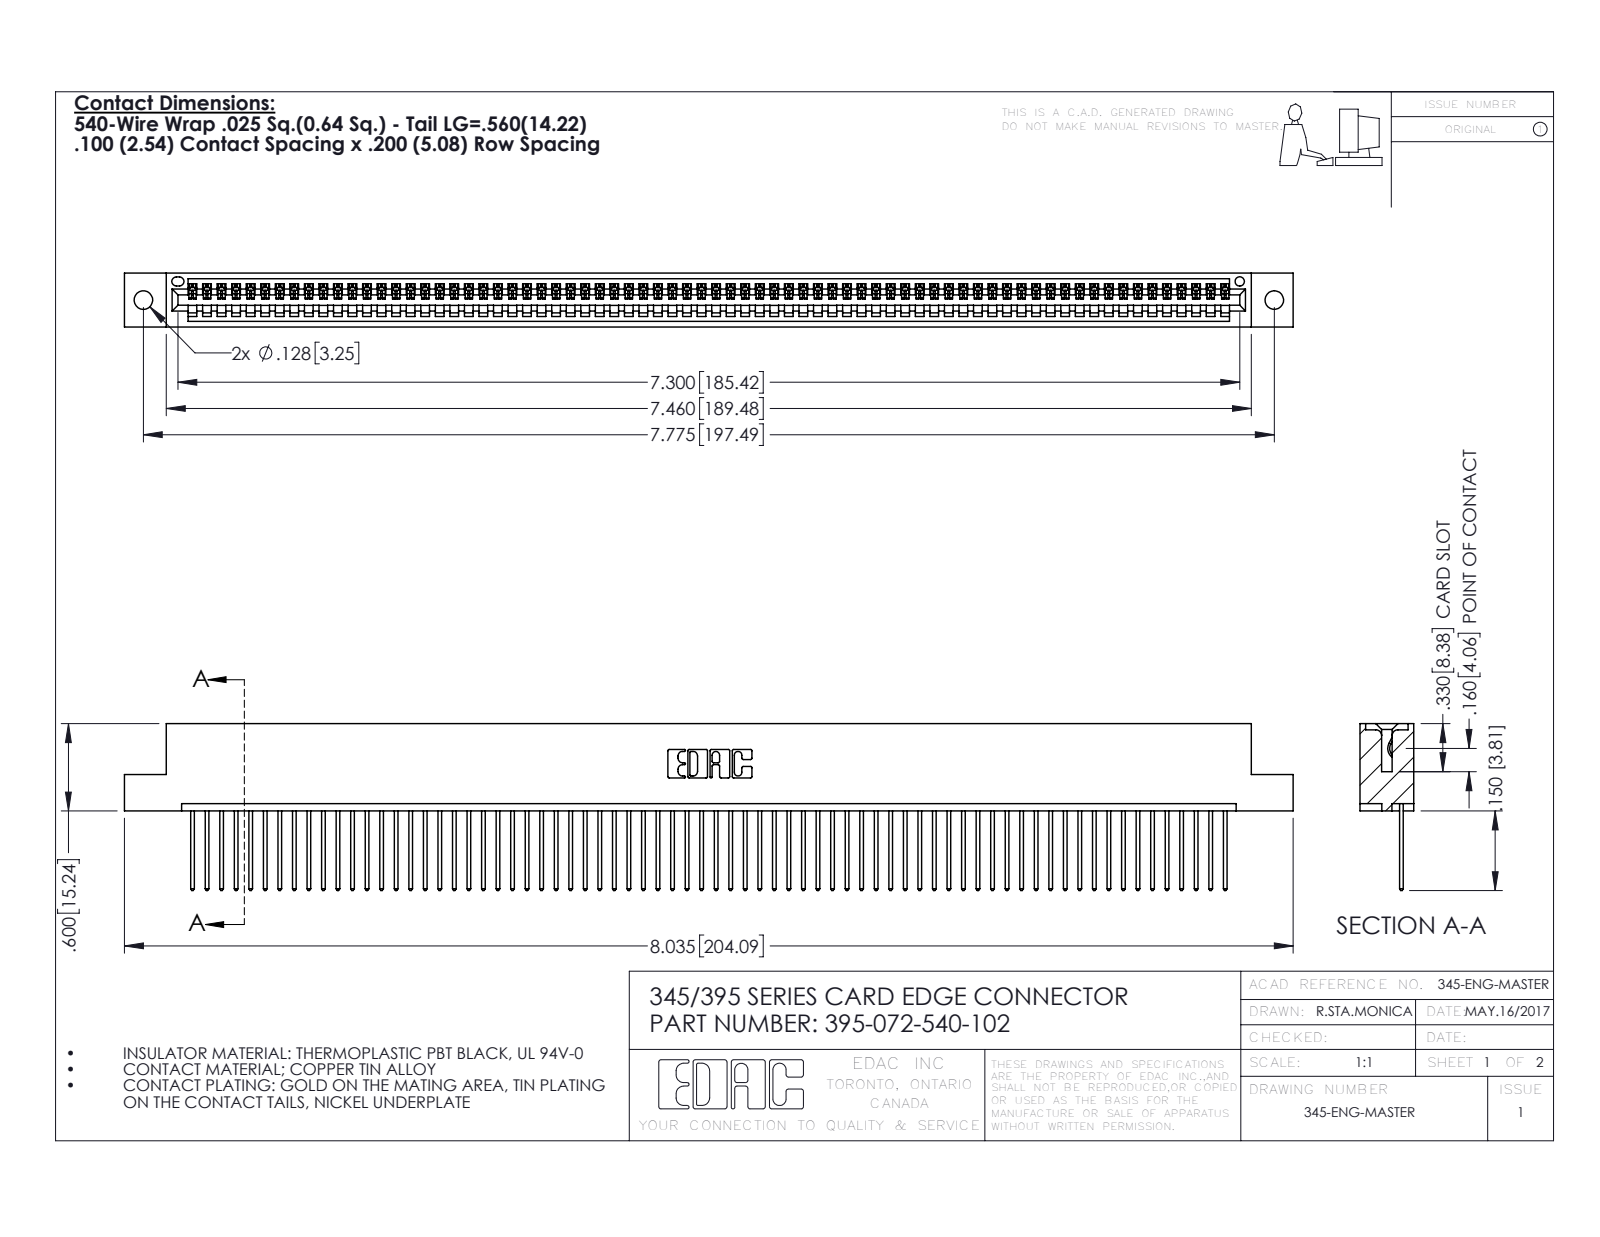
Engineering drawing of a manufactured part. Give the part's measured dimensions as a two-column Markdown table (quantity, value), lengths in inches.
| quantity | value |
| --- | --- |
| part name | 395-072-540-102; 345 Part_Flush Mounting Lugs - 0.128 Dia; 345-292-001_345-293-140 |
| STEP written by | SolidWorks 2016 (CONFIG_CONTROL_DESIGN) |
| units | inches |
| bodies | 73 solids, 4302 faces (2960 planar, 1342 cylindrical, 0 other) |
| overall size | 8.035 × 1.147 × 0.37 |
| volume | 1.202 in³ |
| surface area | 41.86 in² |
| round holes (diameter × count) | 0.128 × 2, 0.064 × 1 |
| partial cylindrical surfaces (radius × count) | 0.006 × 144, 0.01 × 144, 0.01 × 22, 0.007 × 6, 0.031 × 6, 0.026 × 3, 0.031 × 2, 0.04 × 2 |
| main face-to-face distances | 0.072, 0.298, 0.37, 0.098, 0.272, 0.025, 0.2, 0.225, 0.149, 0.072 |
| hole center spacings | 0.27, 7.539, 7.775 |
